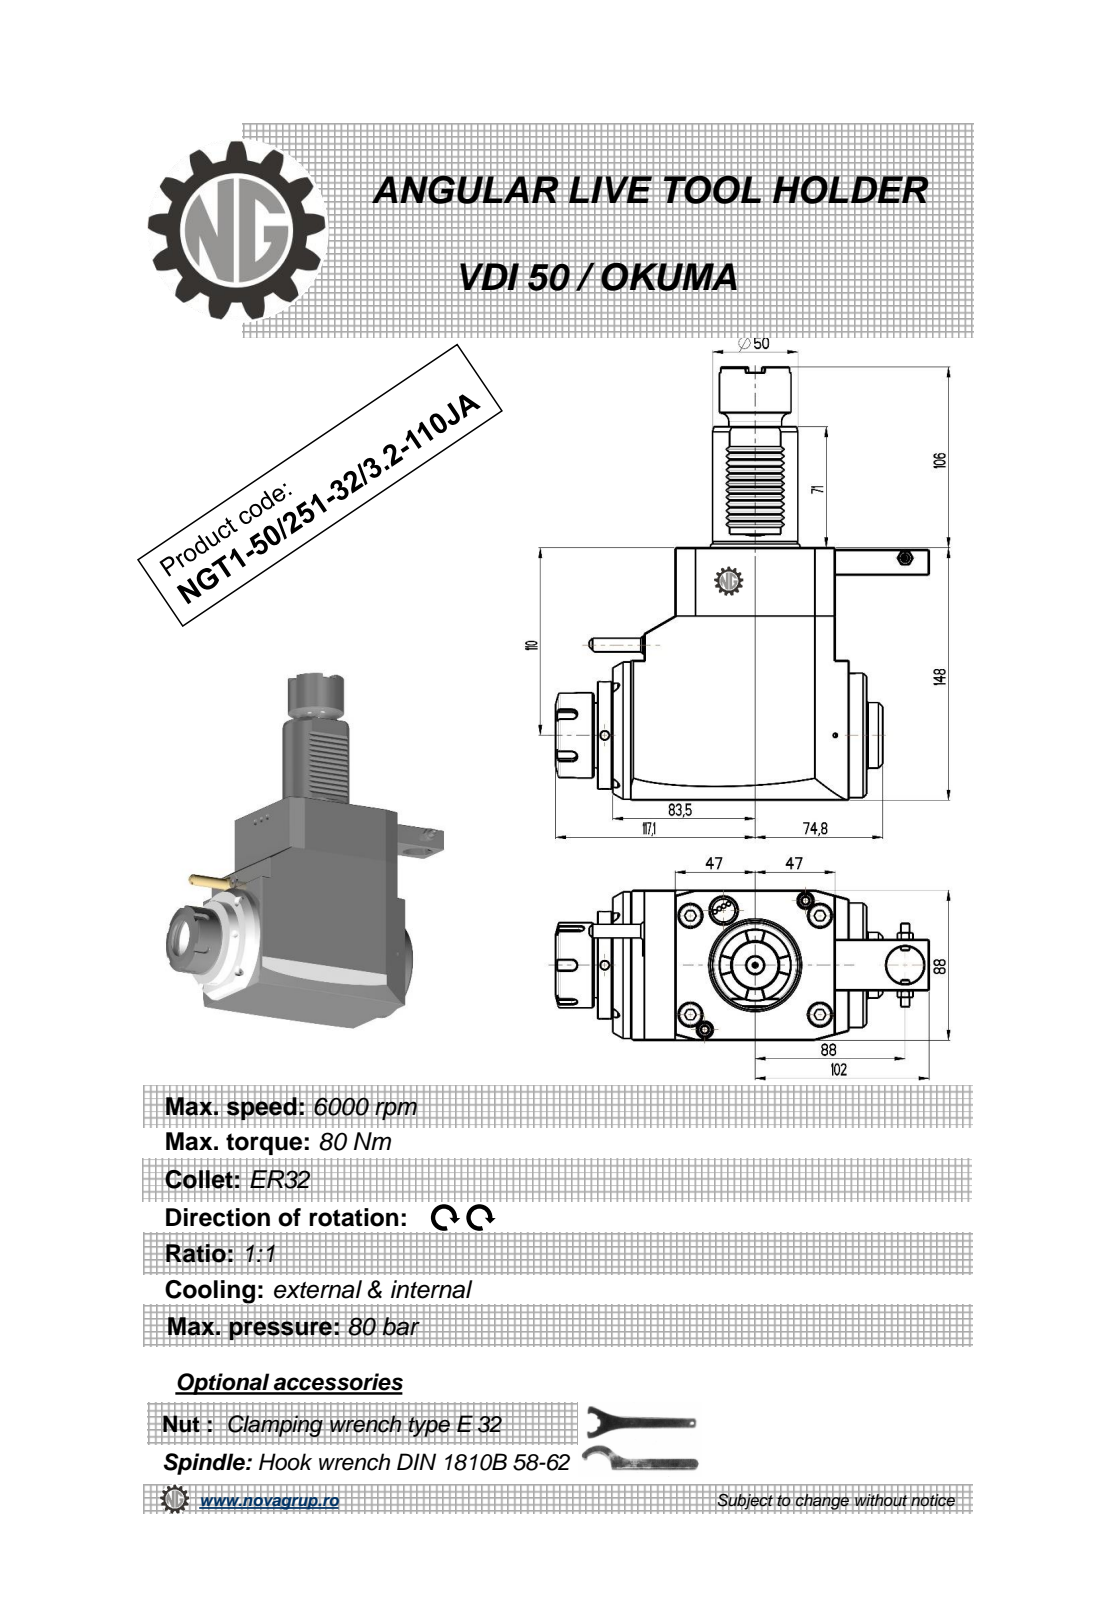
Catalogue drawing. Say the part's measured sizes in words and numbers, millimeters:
The part is named "NGT1_50_251_32_3_2_110JA". Its 3-D file was written by "PRO/ENGINEER BY PARAMETRIC TECHNOLOGY CORPORATION, 2010280 (CONFIG_CONTROL_DESIGN)". It is 1 solid with 484 faces: 216 planar, 102 cylindrical and 166 other. Overall it measures 254 by 219.1 by 88 millimeters. Its volume is 1 855 000 cubic millimeters and its surface area 120 710 square millimeters. Round holes: 3 of diameter 5, 1 of diameter 3, 1 of diameter 4.2, 1 of diameter 4.5, 1 of diameter 9.5, 1 of diameter 12, 1 of diameter 22, 1 of diameter 27, 1 of diameter 28. Round bosses or shafts: 2 of diameter 50, 2 of diameter 5, 1 of diameter 86, 1 of diameter 73, 1 of diameter 63, 1 of diameter 50.5, 1 of diameter 42, 1 of diameter 41. Partial cylindrical surfaces (rounded edges, fillets, slot ends): 12 of radius 0.26, 12 of radius 0.3, 6 of radius 0.2, 5 of radius 3. The main face-to-face distances are 88, 148, 8, 94, 102, 36.5, 130.5, 148.8, 112.3, 18.3. The hole center spacings are 52.46, 56.65, 88, 88.25, 101.5, 176.25.
